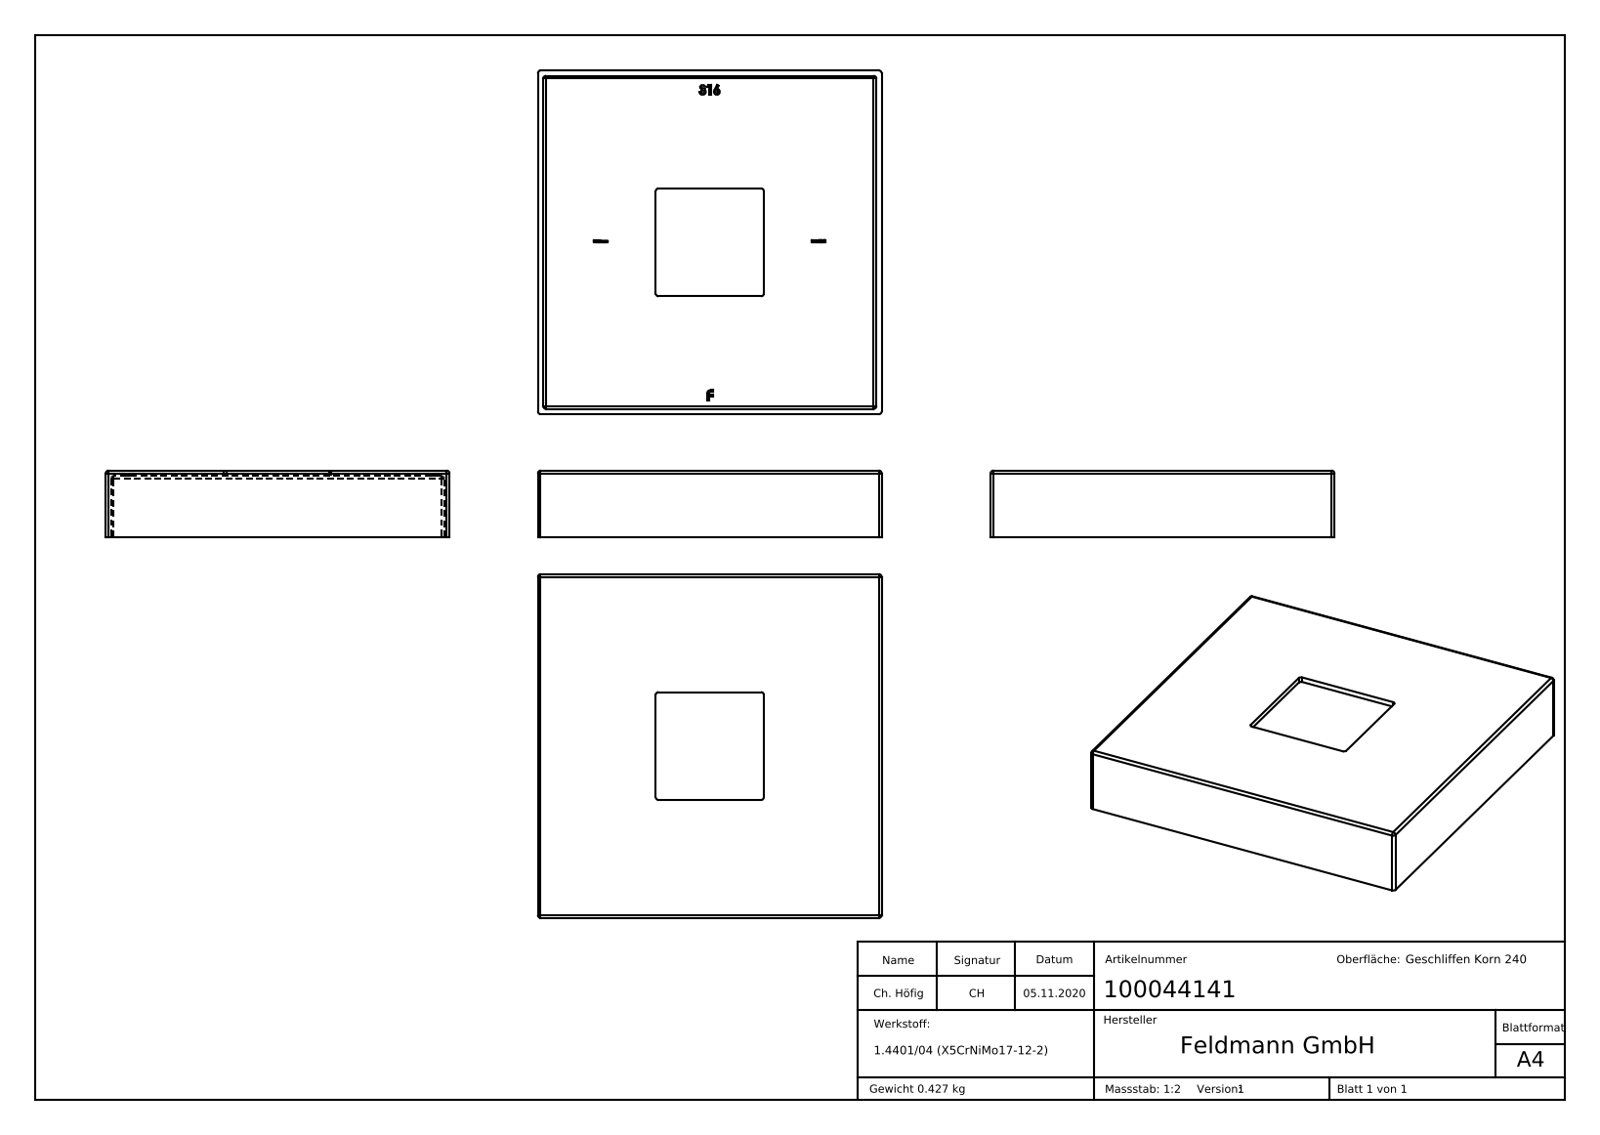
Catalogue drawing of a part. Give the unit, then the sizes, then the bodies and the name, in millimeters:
Units: millimetres
Overall size (bounding box): 129 × 129 × 25
Partial cylindrical surfaces — rounded edges, fillets, slot ends (radius × count): R1 ×20
Main face-to-face distances: 2, 127, 129, 125, 23, 25, 44.25, 84.75, 42.25, 82.75
Volume: 53 364 mm³ · Surface area: 54 215 mm²
Bodies: 1 solid, 305 faces (179 planar, 20 cylindrical, 106 other)
Part name (STEP PRODUCT): 100044141
STEP written by: SolidWorks 2018 (CONFIG_CONTROL_DESIGN)
